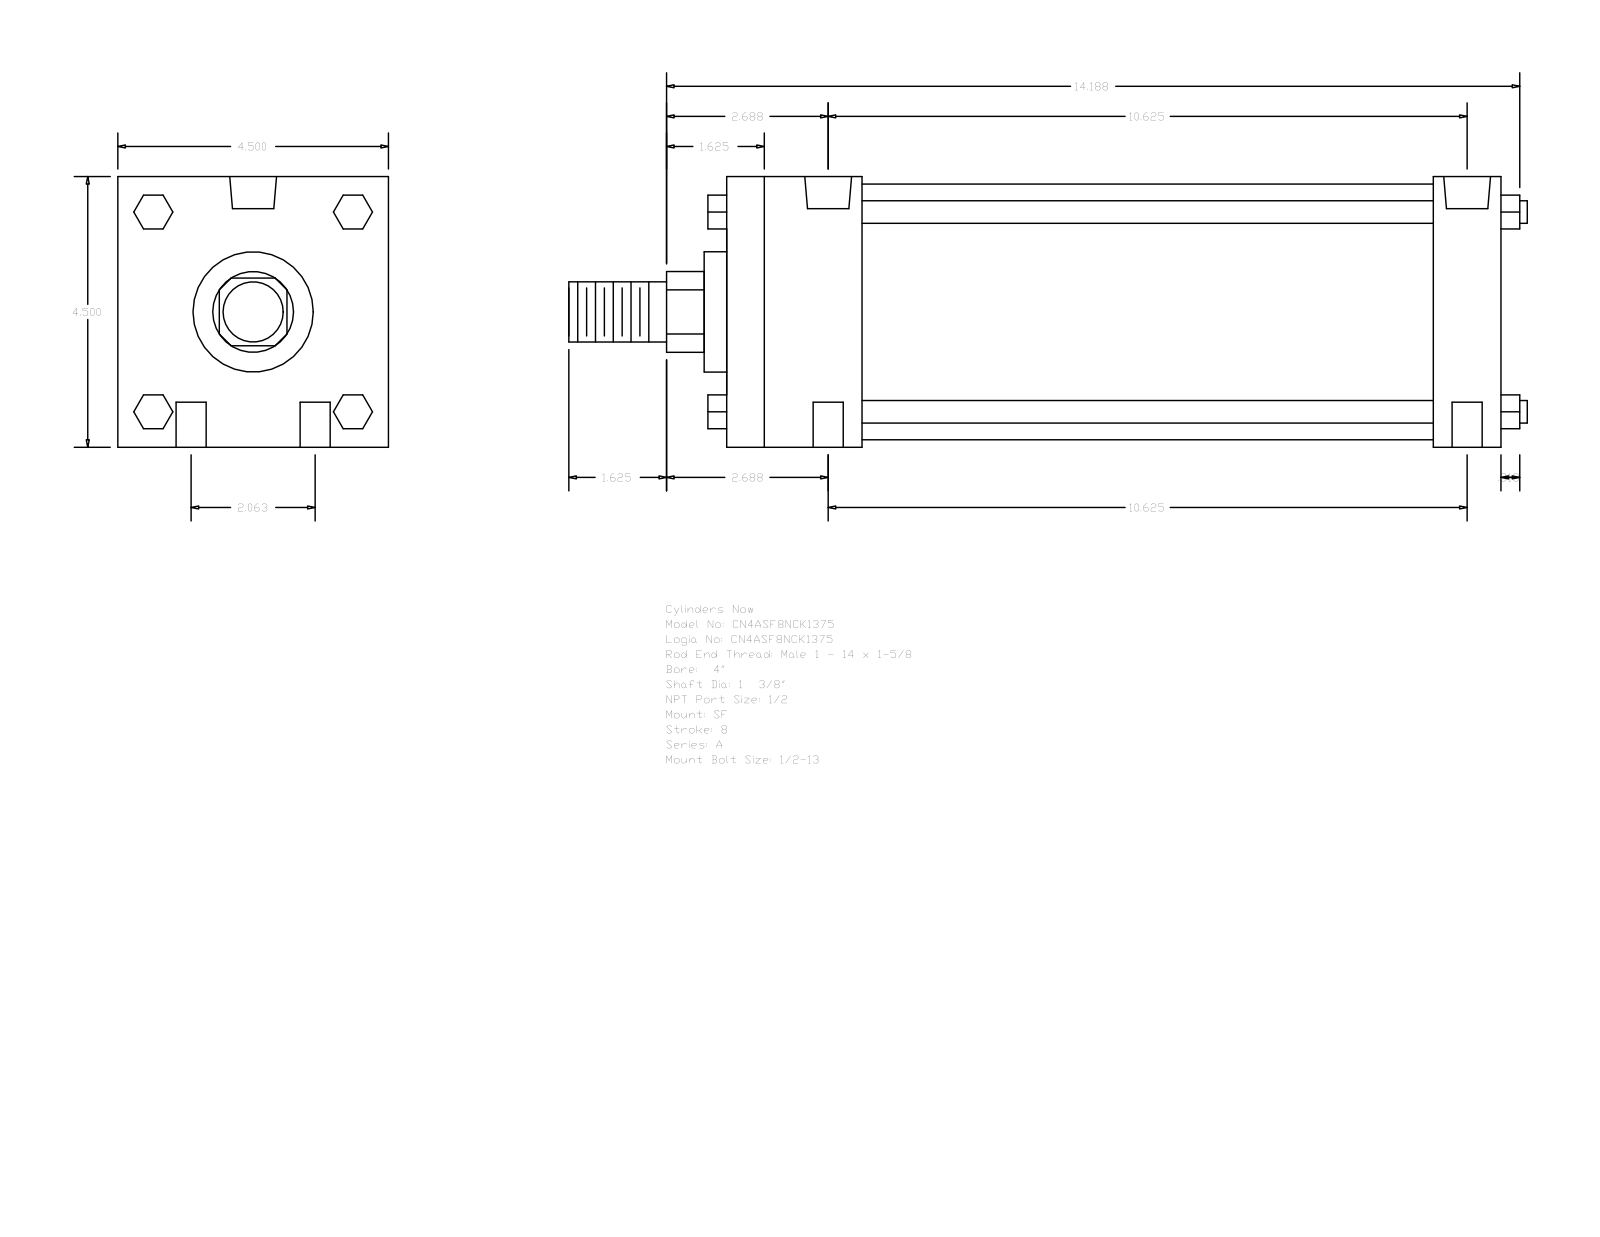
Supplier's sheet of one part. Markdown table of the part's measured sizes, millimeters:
| quantity | value |
| --- | --- |
| part name | A_SF__0400_1.375 |
| STEP written by | GSSL Pune (CONFIG_CONTROL_DESIGN) |
| units | millimeters |
| bodies | 0 solids, 124 faces (94 planar, 30 cylindrical, 0 other) |
| overall size | 404.81 × 114.3 × 114.3 |
| round holes (diameter × count) | 12.7 × 4, 8.73 × 2, 19.77 × 2 |
| round bosses / shafts (diameter × count) | 9.53 × 4, 107.95 × 1, 50.8 × 1, 34.92 × 1, 25.4 × 1 |
| partial cylindrical surfaces (radius × count) | 17.06 × 1 |
| main face-to-face distances | 114.3, 327.03, 57.15, 28.58, 298.45, 241.3, 269.88, 66.67, 14.29, 9.52 |
| hole center spacings | 26.19, 271.15, 269.88, 52.38, 274.92, 263.52 |
